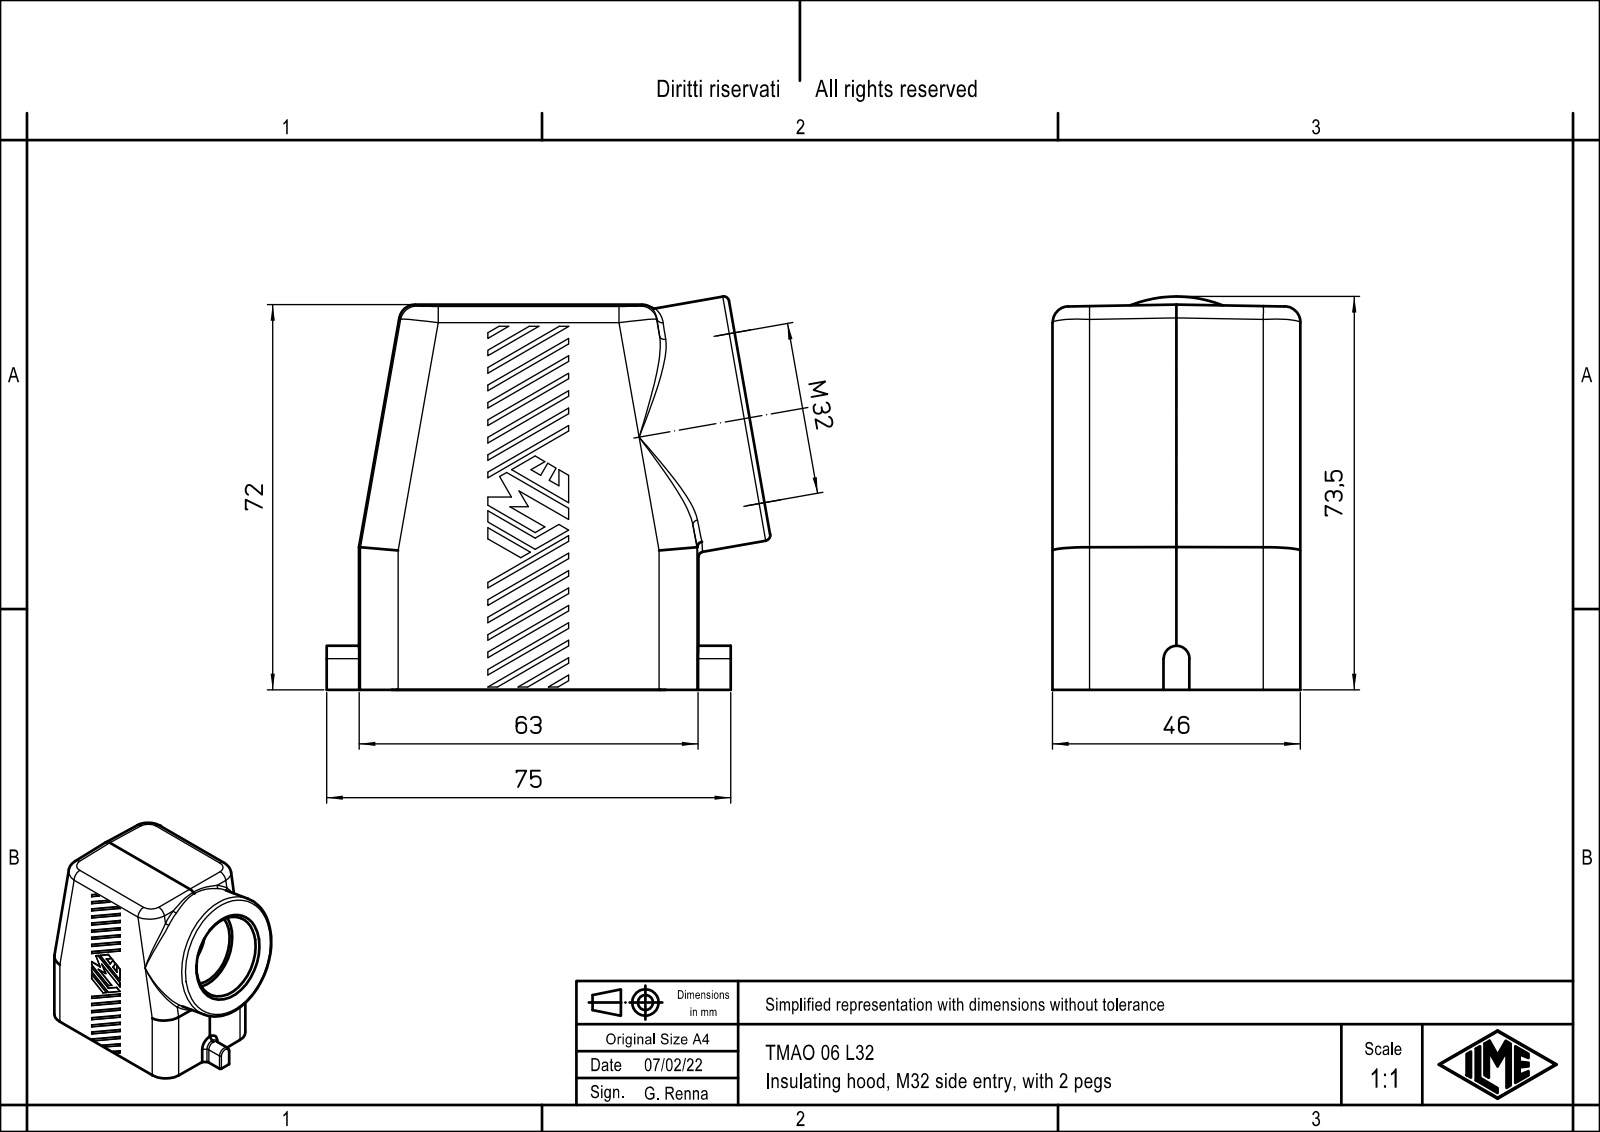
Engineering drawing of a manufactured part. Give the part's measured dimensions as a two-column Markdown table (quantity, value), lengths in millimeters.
| quantity | value |
| --- | --- |
| part name | TMAO_06_L32 |
| STEP written by | Creo Elements/Direct Modeling 20.1B 02-Apr-2019 (C) Parametric Technology GmbH (AUTOMOTIVE_DESIGN) |
| units | millimeters |
| bodies | 1 solid, 414 faces (103 planar, 261 cylindrical, 50 other) |
| overall size | 84.33 × 73.49 × 46.3 |
| volume | 99 251 mm³ |
| surface area | 32 952 mm² |
| round holes (diameter × count) | 6.1 × 4, 28 × 1, 30.6 × 1 |
| round bosses / shafts (diameter × count) | 46 × 1 |
| partial cylindrical surfaces (radius × count) | 0.15 × 128, 7 × 8, 3 × 6, 0.5 × 4, 1 × 4, 1.5 × 4, 2 × 4, 2.4 × 1 |
| main face-to-face distances | 46, 7.99, 63, 8, 26.51, 46.15, 46.3, 20.75, 25.55, 20.6 |
| hole center spacings | 27, 44, 51.62 |
